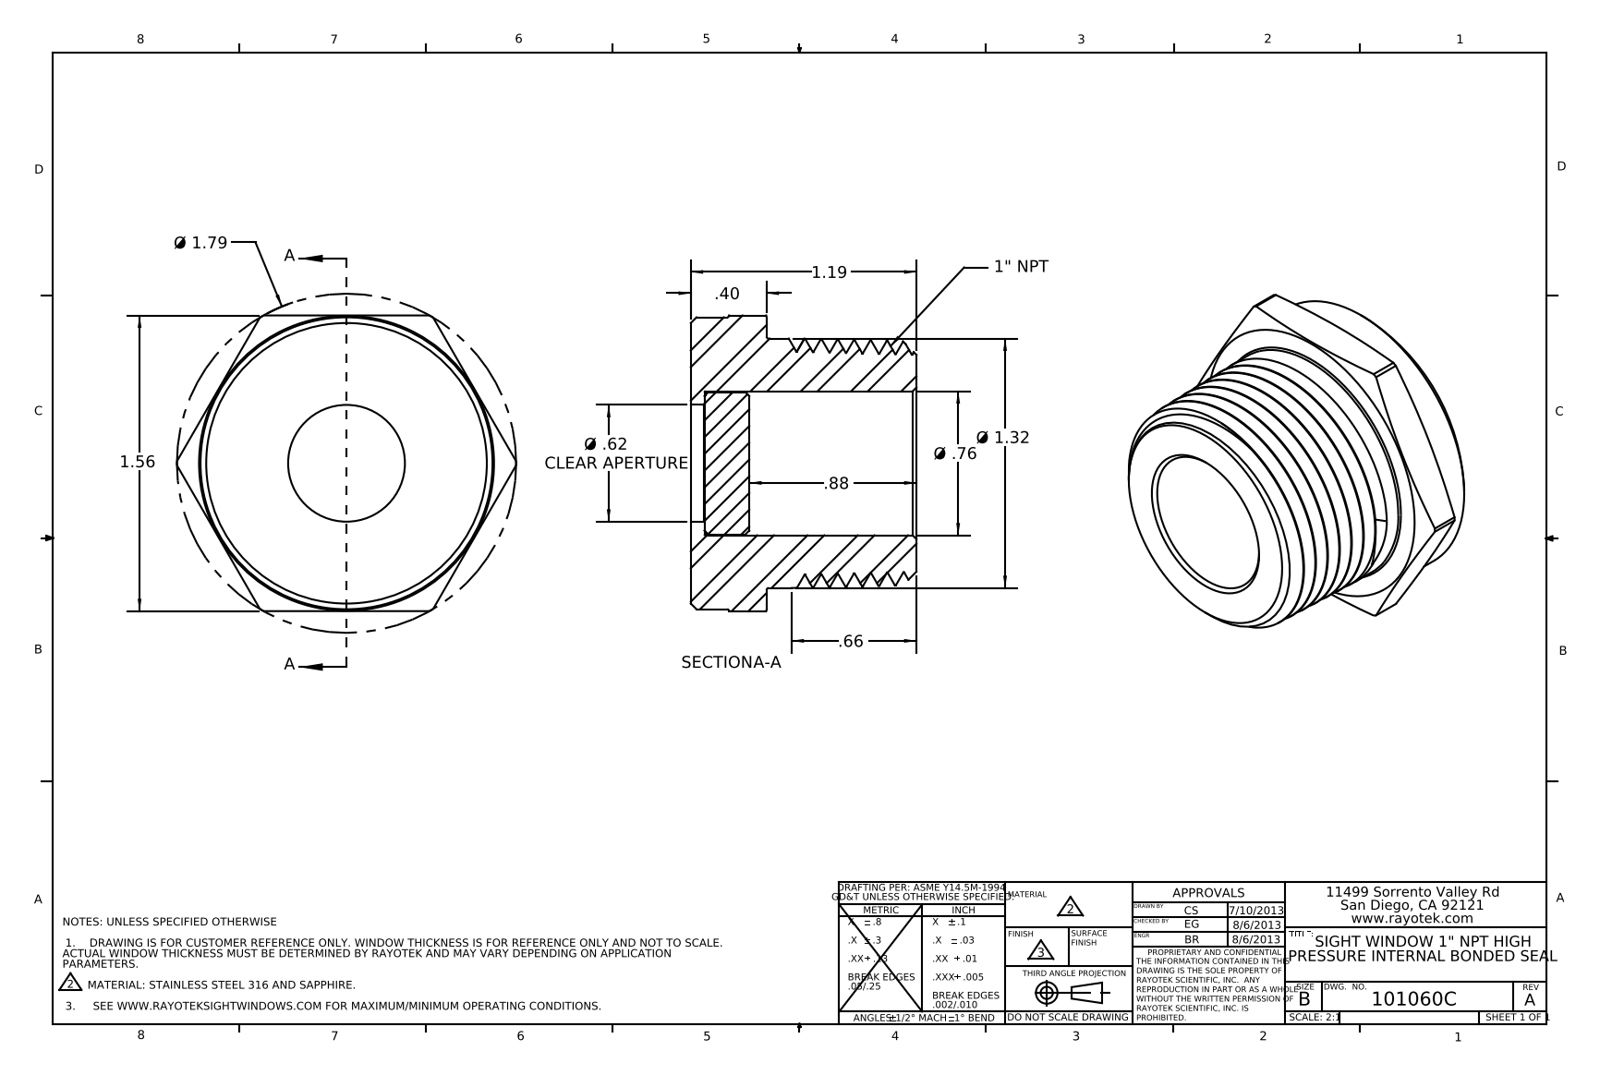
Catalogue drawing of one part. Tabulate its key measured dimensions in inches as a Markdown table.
| quantity | value |
| --- | --- |
| part name | 101060; 402060; 403060 |
| STEP written by | SolidWorks 2012 (AUTOMOTIVE_DESIGN) |
| units | inches |
| bodies | 2 solids, 73 faces (15 planar, 17 cylindrical, 41 other) |
| overall size | 1.789 × 1.56 × 1.19 |
| volume | 1.324 in³ |
| surface area | 14.59 in² |
| round holes (diameter × count) | 0.616 × 1, 0.76 × 1 |
| round bosses / shafts (diameter × count) | 1.54 × 1, 1.316 × 1, 0.75 × 1 |
| partial cylindrical surfaces (radius × count) | 0.895 × 1 |
| main face-to-face distances | 0.072, 1.19, 1.118, 1.56, 0.4, 0.328, 0.79, 0.308, 0.236, 0.092 |
